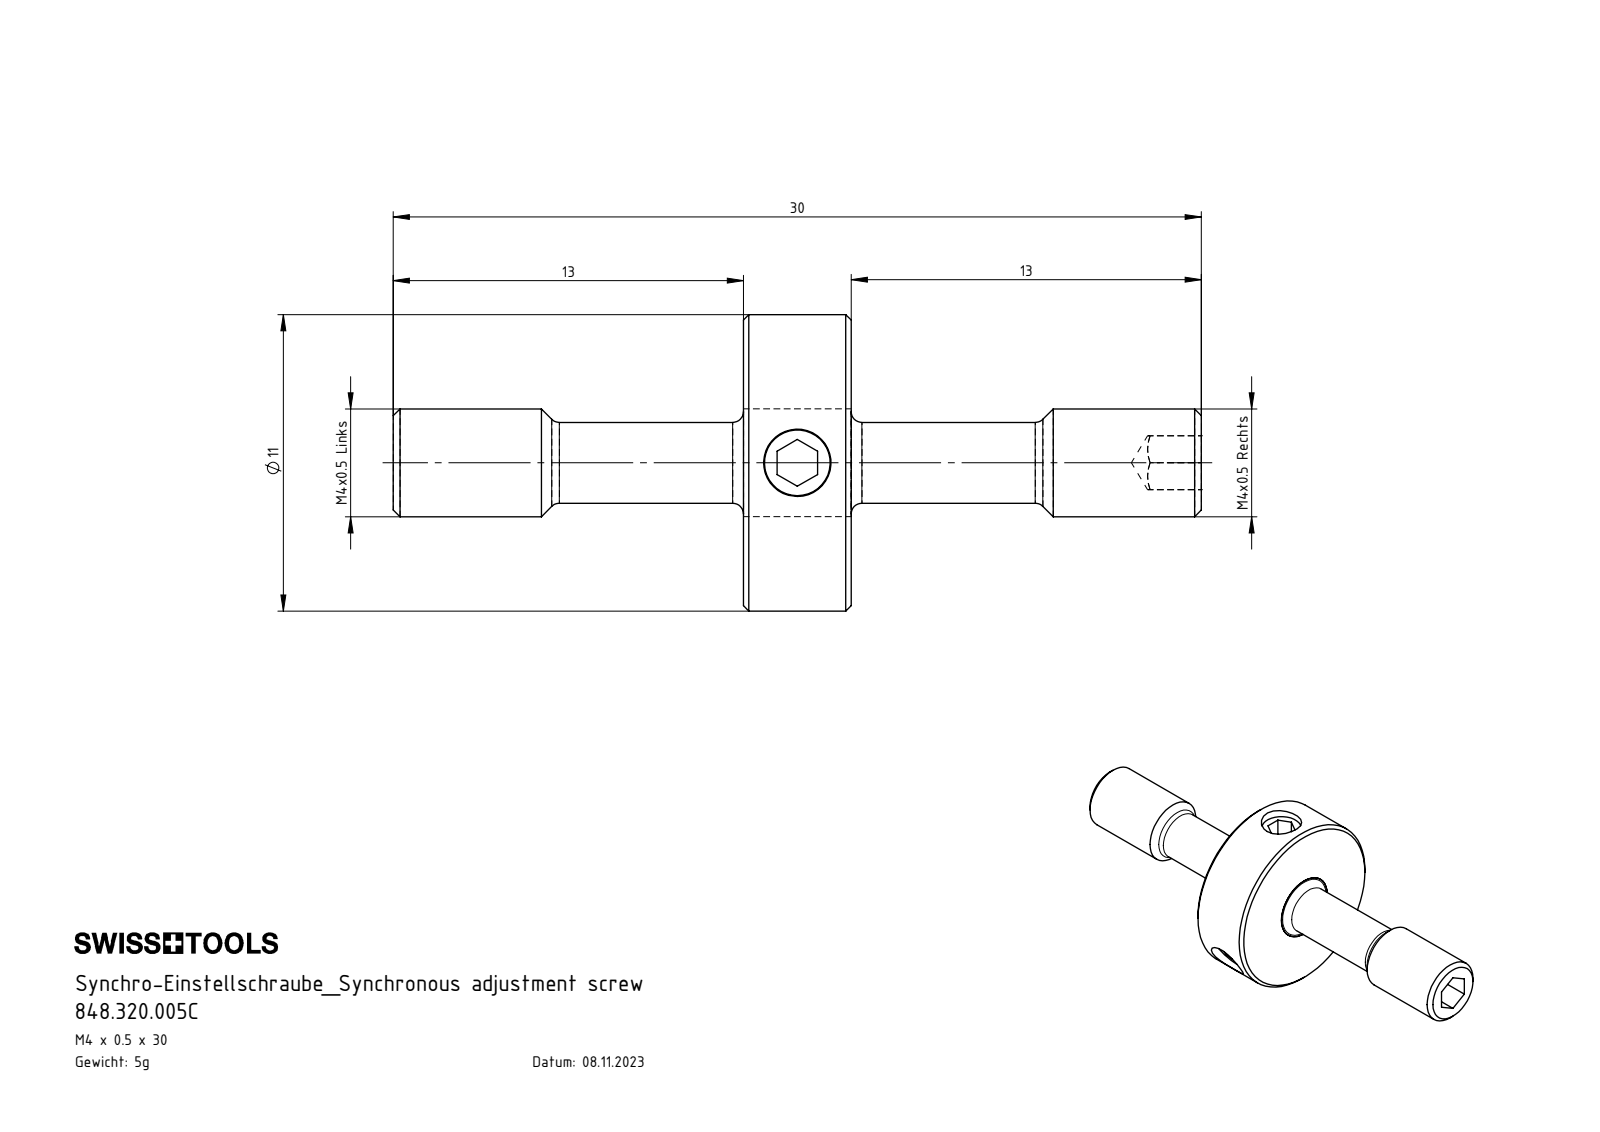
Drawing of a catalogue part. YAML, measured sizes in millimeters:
part_name: "Z32-ER3.001.030_A; 848.320.005C; Z25-ER3.002.004_A; ISO 4026 - M3 x 3"
step_written_by: "SolidWorks 2022 (AUTOMOTIVE_DESIGN)"
units: millimeters
bodies: {solids: 5, faces: 99, planar: 39, cylindrical: 26, other: 34}
overall_size: [30, 11, 11]
volume: 614
surface_area: 925
round_holes:
  - {diameter: 2.5, count: 3}
round_bosses_or_shafts:
  - {diameter: 3, count: 4}
  - {diameter: 11, count: 1}
  - {diameter: 4, count: 1}
face_to_face_distances: [4, 13, 17, 1.5, 2, 14.25, 15.75, 1.25, 2.75, 3]
